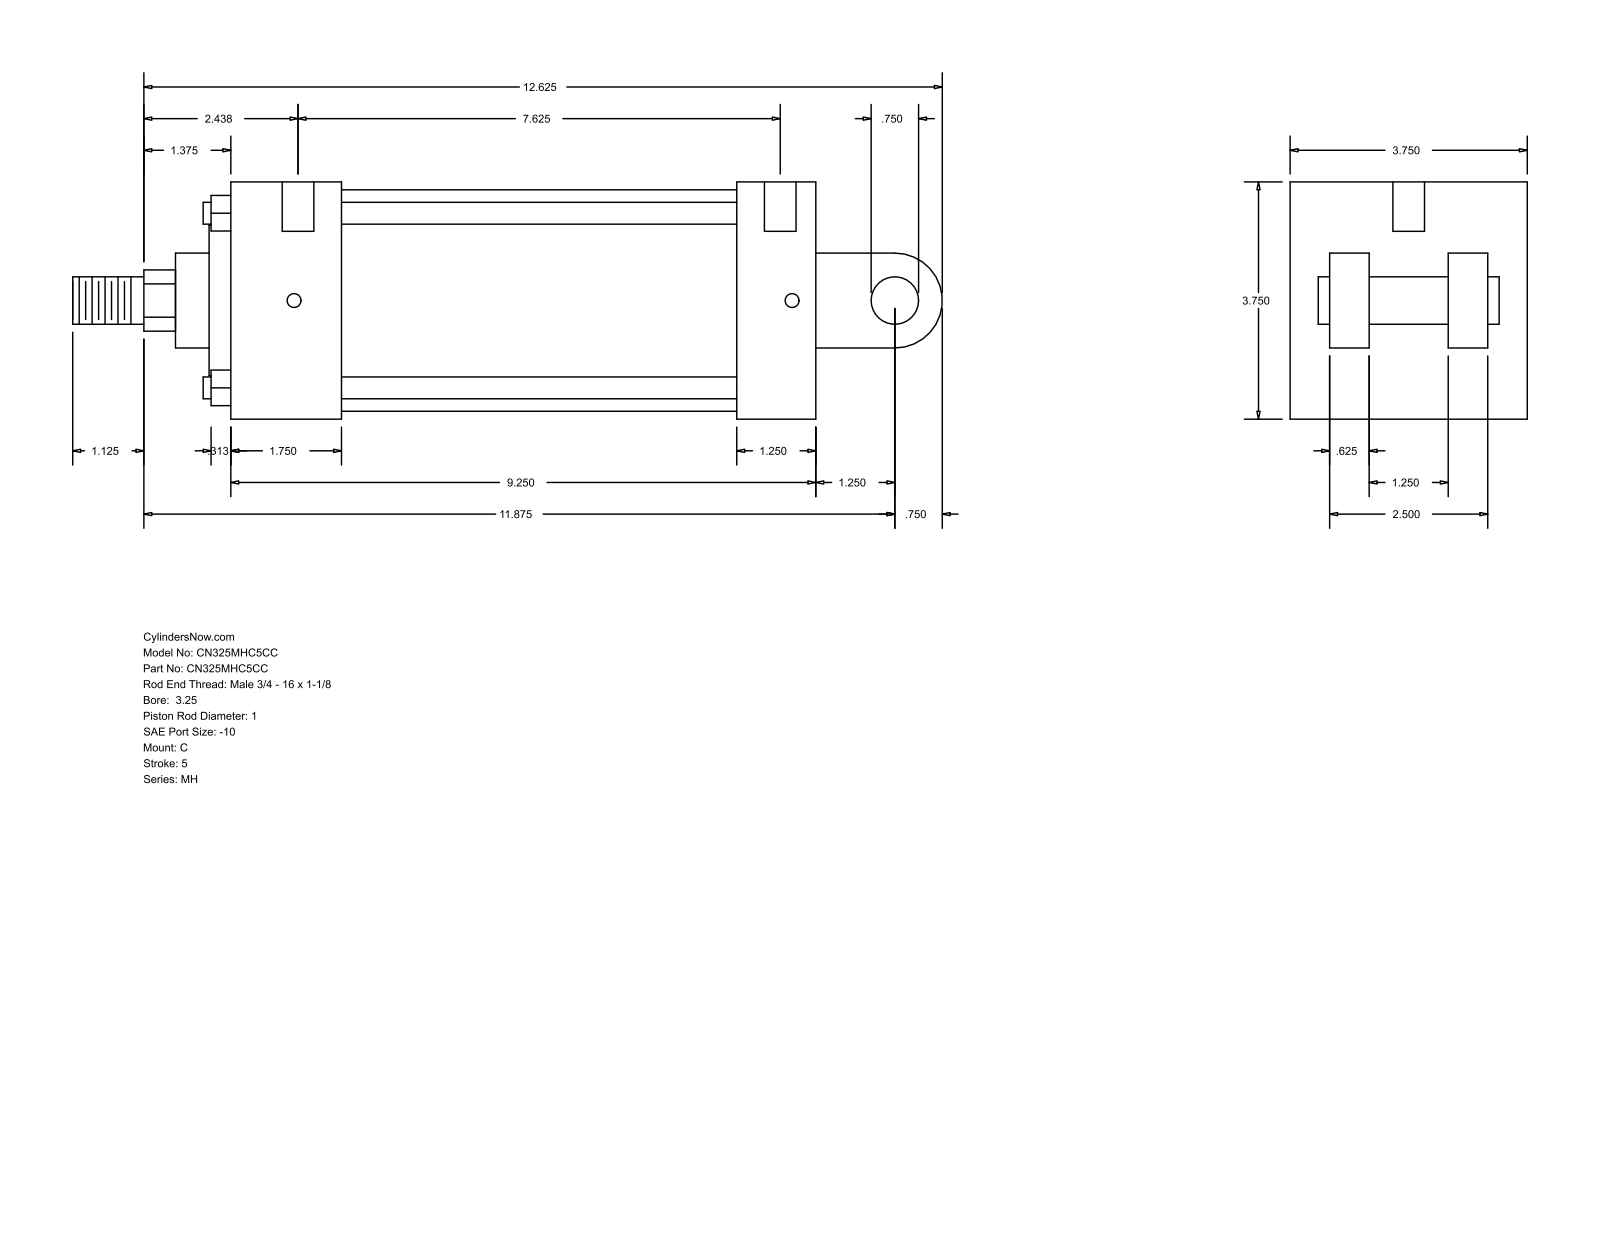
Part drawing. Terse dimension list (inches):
name: MH_C__0325_1
written by: GSSL Pune (CONFIG_CONTROL_DESIGN)
unit: in
bodies: 0 solids, 101 faces (71 planar, 30 cylindrical, 0 other)
size: 13.75 × 3.75 × 3.75
holes: 4× ⌀0.219, 2× ⌀0.5
bosses: 4× ⌀0.345, 2× ⌀0.75, 1× ⌀3.5, 1× ⌀2.375, 1× ⌀1.5, 1× ⌀1
rounds: 1× R0.484, 1× R0.75
face distances: 3.75, 0.625, 9.25, 2.5, 1.25, 3.125, 1.25, 1.875, 1.75, 8
hole spacings: 7.875, 0.062, 0.187, 7.625, 7.687, 7.813
